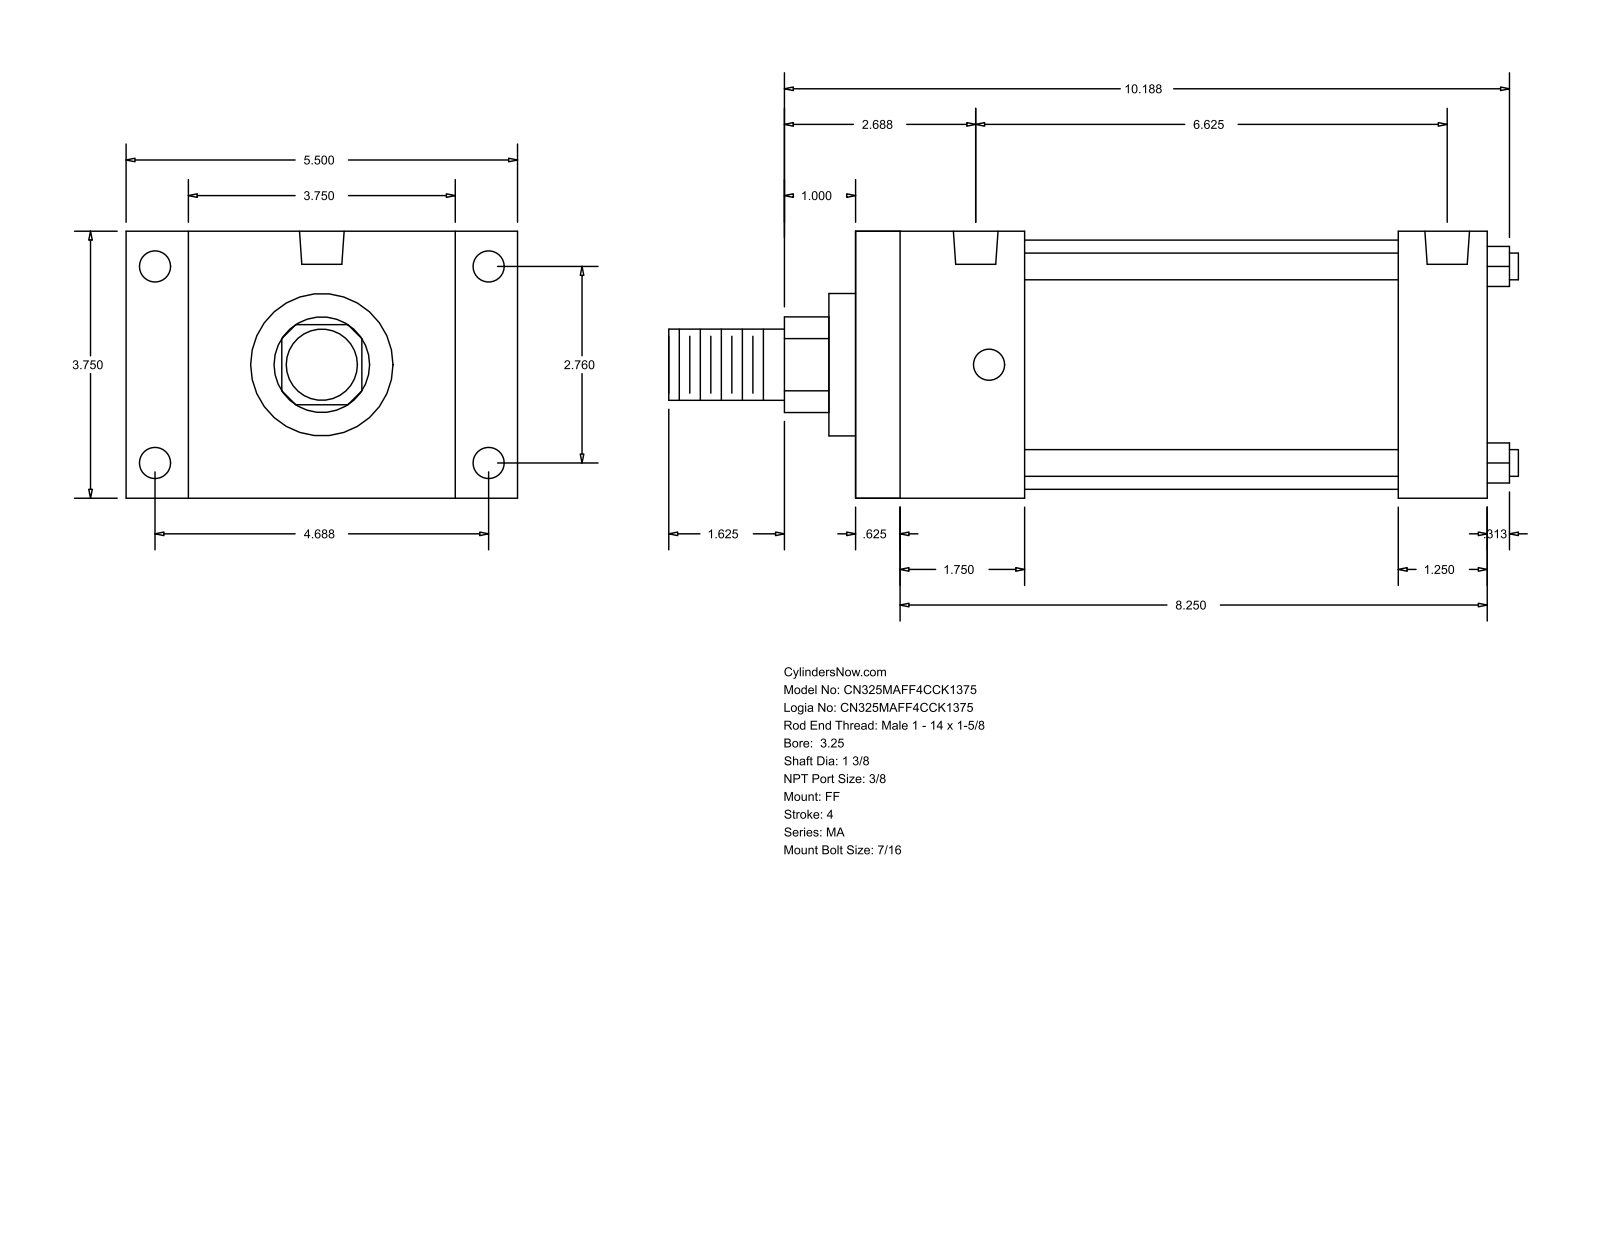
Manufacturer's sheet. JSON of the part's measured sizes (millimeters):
{"part_name": "MA_FF__0325_1.375", "step_written_by": "GSSL Pune (CONFIG_CONTROL_DESIGN)", "units": "millimeters", "bodies": {"solids": 0, "faces": 92, "planar": 64, "cylindrical": 28, "other": 0}, "overall_size": [303.21, 139.7, 95.25], "round_holes": [[11.11, 8], [15.93, 2]], "round_bosses_or_shafts": [[9.53, 4], [88.9, 1], [50.8, 1], [34.92, 1], [25.4, 1]], "partial_cylinders_radius": [[17.06, 1]], "face_to_face_distances": [95.24, 225.42, 15.87, 209.55, 22.23, 117.47, 60.32, 193.67, 44.45, 177.8], "hole_center_spacings": [70.1, 119.06, 138.16, 158.75, 4.76, 4.77, 163.51, 163.52]}
